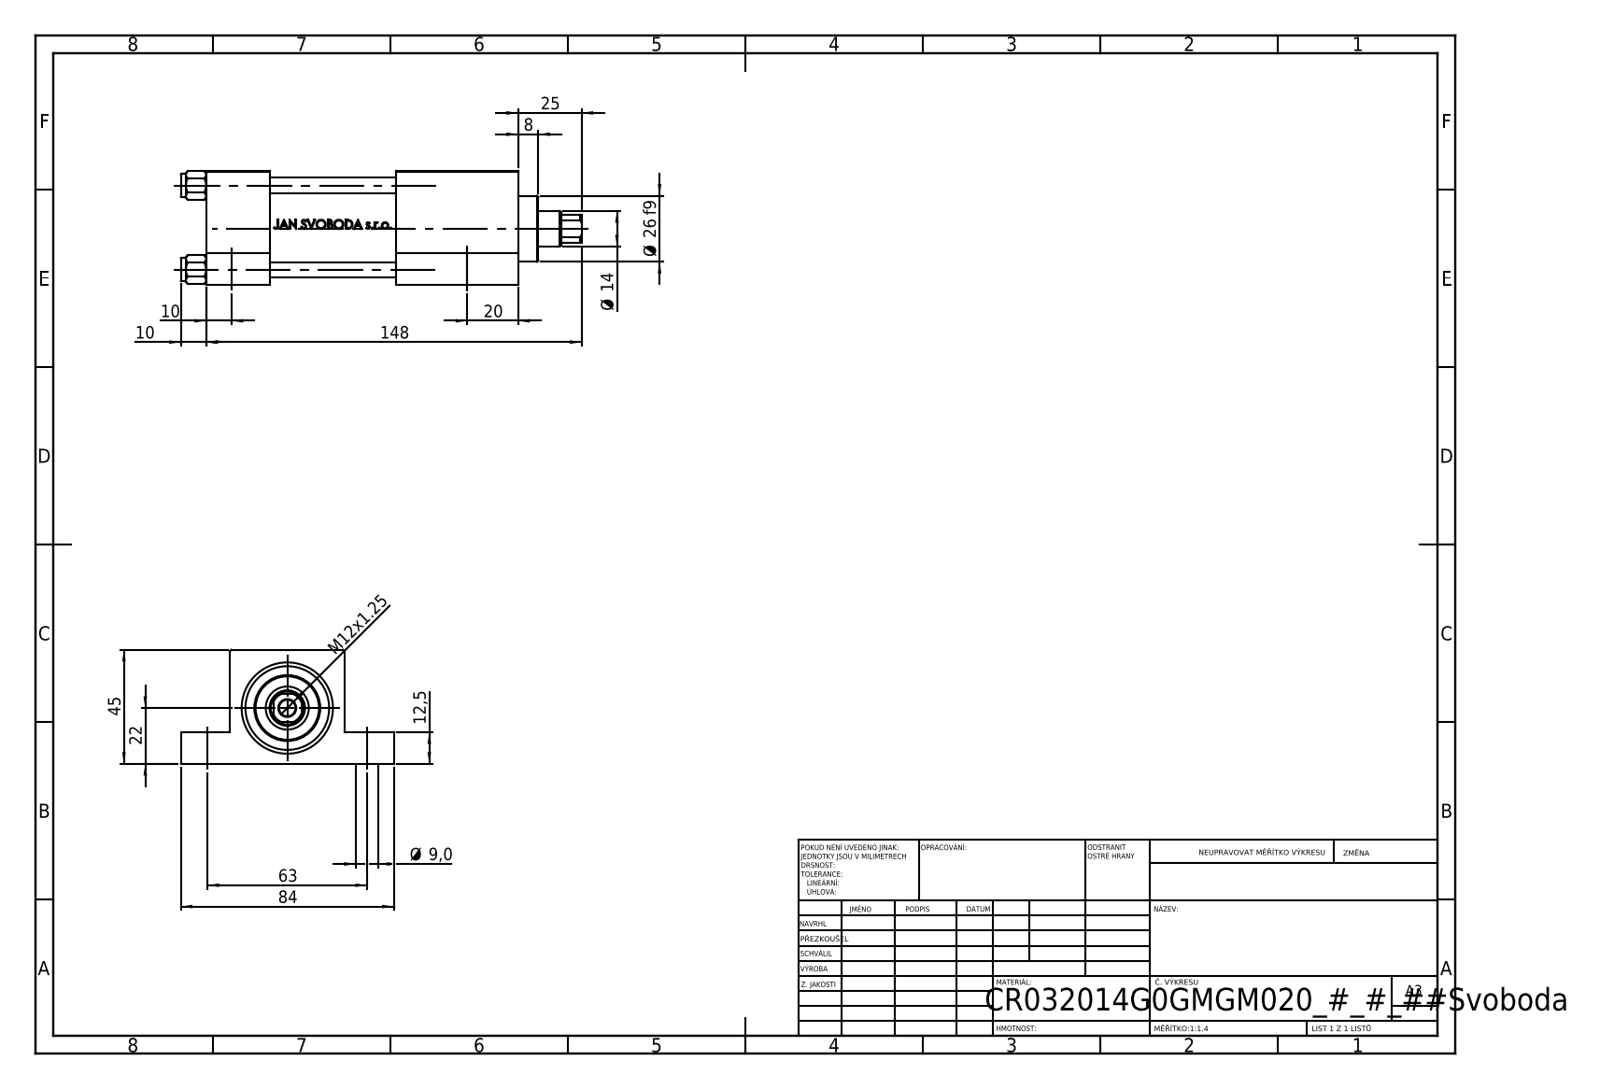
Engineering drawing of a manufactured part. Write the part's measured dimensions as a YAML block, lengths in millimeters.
part_name: "V215_VC_A; V215CR_G_TYCINKA; V215CR_G_Body; V215CR_VCP_G (+1 more)"
step_written_by: "SolidWorks 2019 (CONFIG_CONTROL_DESIGN)"
units: millimeters
bodies: {solids: 11, faces: 1086, planar: 430, cylindrical: 124, other: 532}
overall_size: [158, 84, 45]
volume: 227955
surface_area: 74460
round_holes:
  - {diameter: 6, count: 4}
  - {diameter: 9, count: 4}
  - {diameter: 7, count: 2}
  - {diameter: 13.16, count: 2}
  - {diameter: 20, count: 2}
  - {diameter: 6.5, count: 1}
  - {diameter: 14, count: 1}
  - {diameter: 17, count: 1}
  - {diameter: 24, count: 1}
  - {diameter: 32, count: 1}
  - {diameter: 33, count: 1}
round_bosses_or_shafts:
  - {diameter: 9, count: 4}
  - {diameter: 38, count: 1}
  - {diameter: 26, count: 1}
partial_cylinders:
  - {radius: 6.5, count: 1}
face_to_face_distances: [45, 25, 12.5, 32.5, 98, 123, 19.5, 64.5, 50, 75]
hole_center_spacings: [33.2, 23.13, 23.83, 46.95, 63, 93, 112.33, 75.5]
